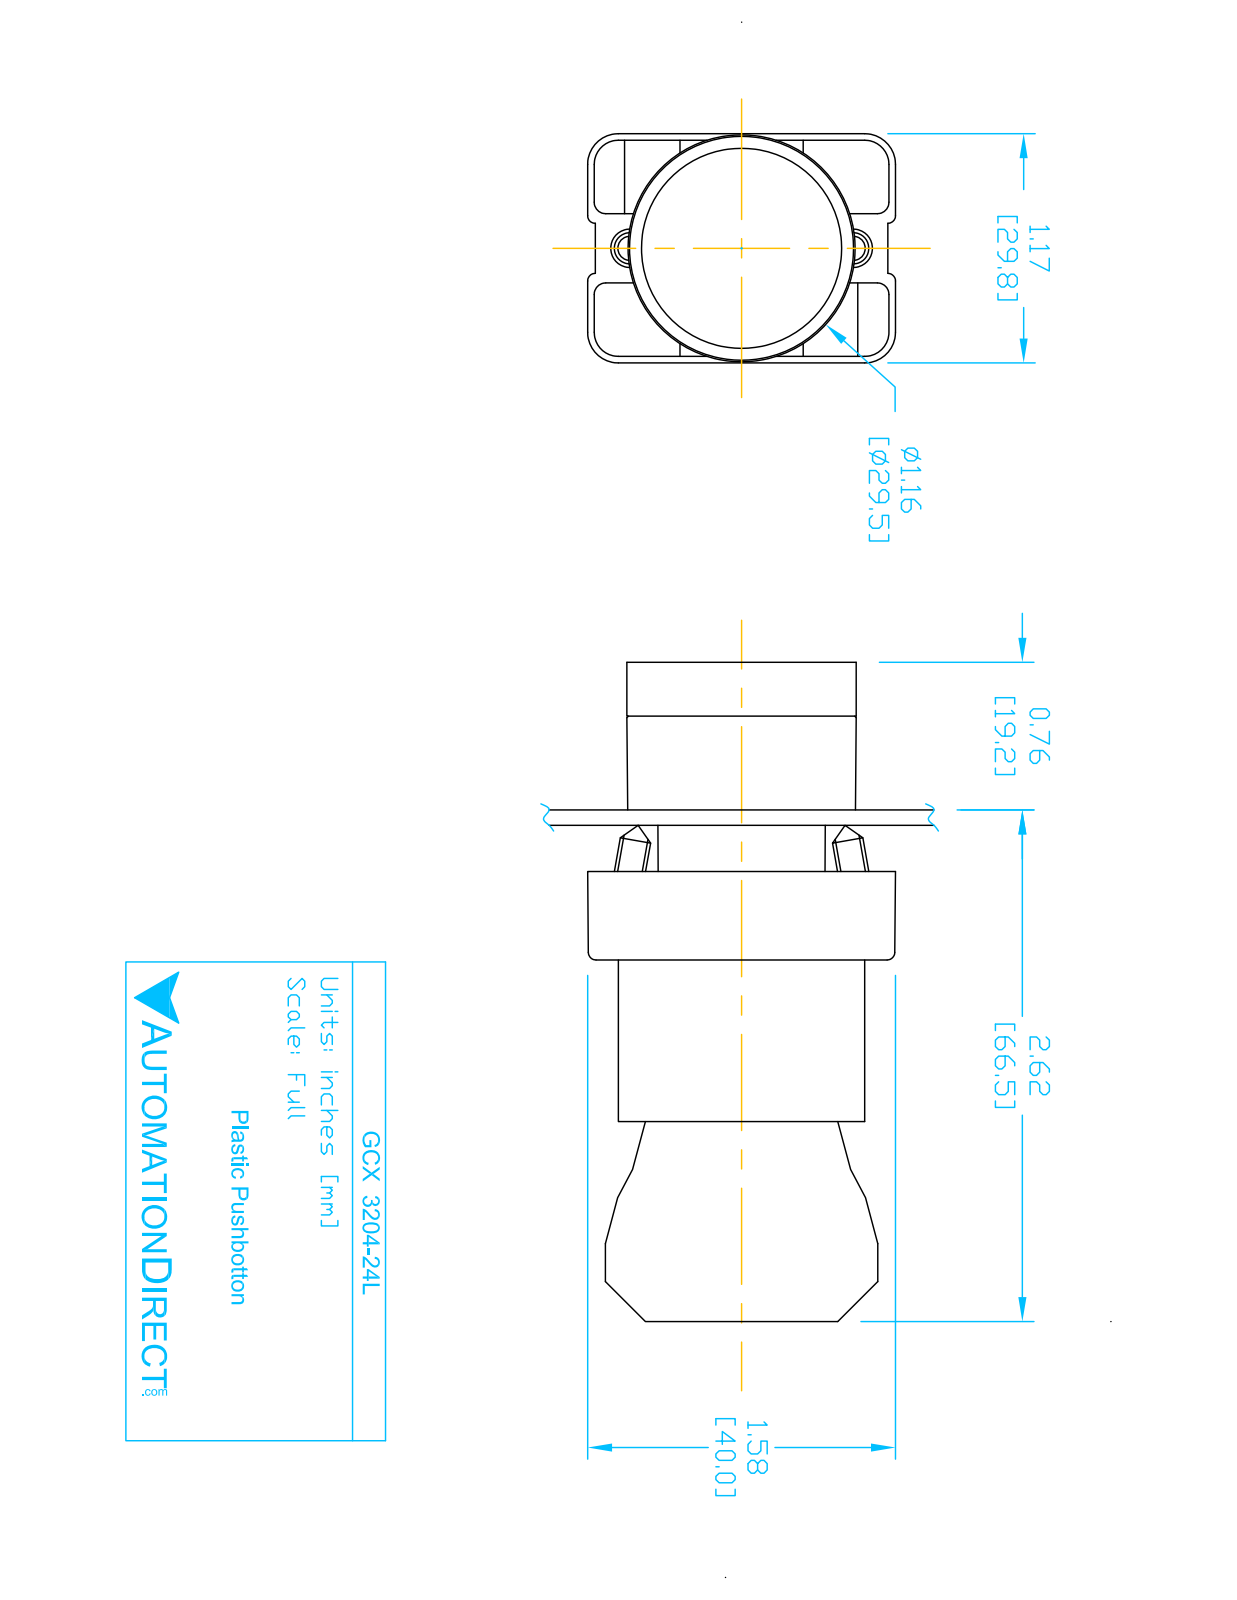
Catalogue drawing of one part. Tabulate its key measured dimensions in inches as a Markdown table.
| quantity | value |
| --- | --- |
| part name | GCX3204L OPERATOR; ECX1050; ecx1040; ECX3029-2 (+1 more) |
| STEP written by | SolidWorks 2016 (AUTOMOTIVE_DESIGN) |
| units | inches |
| bodies | 8 solids, 431 faces (252 planar, 148 cylindrical, 31 other) |
| overall size | 3.319 × 1.581 × 1.177 |
| volume | 2.794 in³ |
| surface area | 38.77 in² |
| round holes (diameter × count) | 0.079 × 2, 0.124 × 2, 0.13 × 2, 0.087 × 1, 0.197 × 1, 0.469 × 1, 0.878 × 1, 0.888 × 1, 1.024 × 1 |
| round bosses / shafts (diameter × count) | 0.157 × 4, 1.175 × 1, 1.004 × 1, 0.945 × 1, 0.856 × 1, 0.78 × 1, 0.504 × 1 |
| partial cylindrical surfaces (radius × count) | 0.059 × 24, 0.041 × 12, 0.124 × 12, 0.157 × 12, 0.039 × 8, 0.128 × 2, 0.02 × 1, 0.063 × 1 |
| main face-to-face distances | 0.827, 0.579, 2.02, 1.193, 1.171, 0.276, 2.295, 1.469, 0.031, 0.033 |
| hole center spacings | 0.236, 0.544, 0.472, 0.49 |
